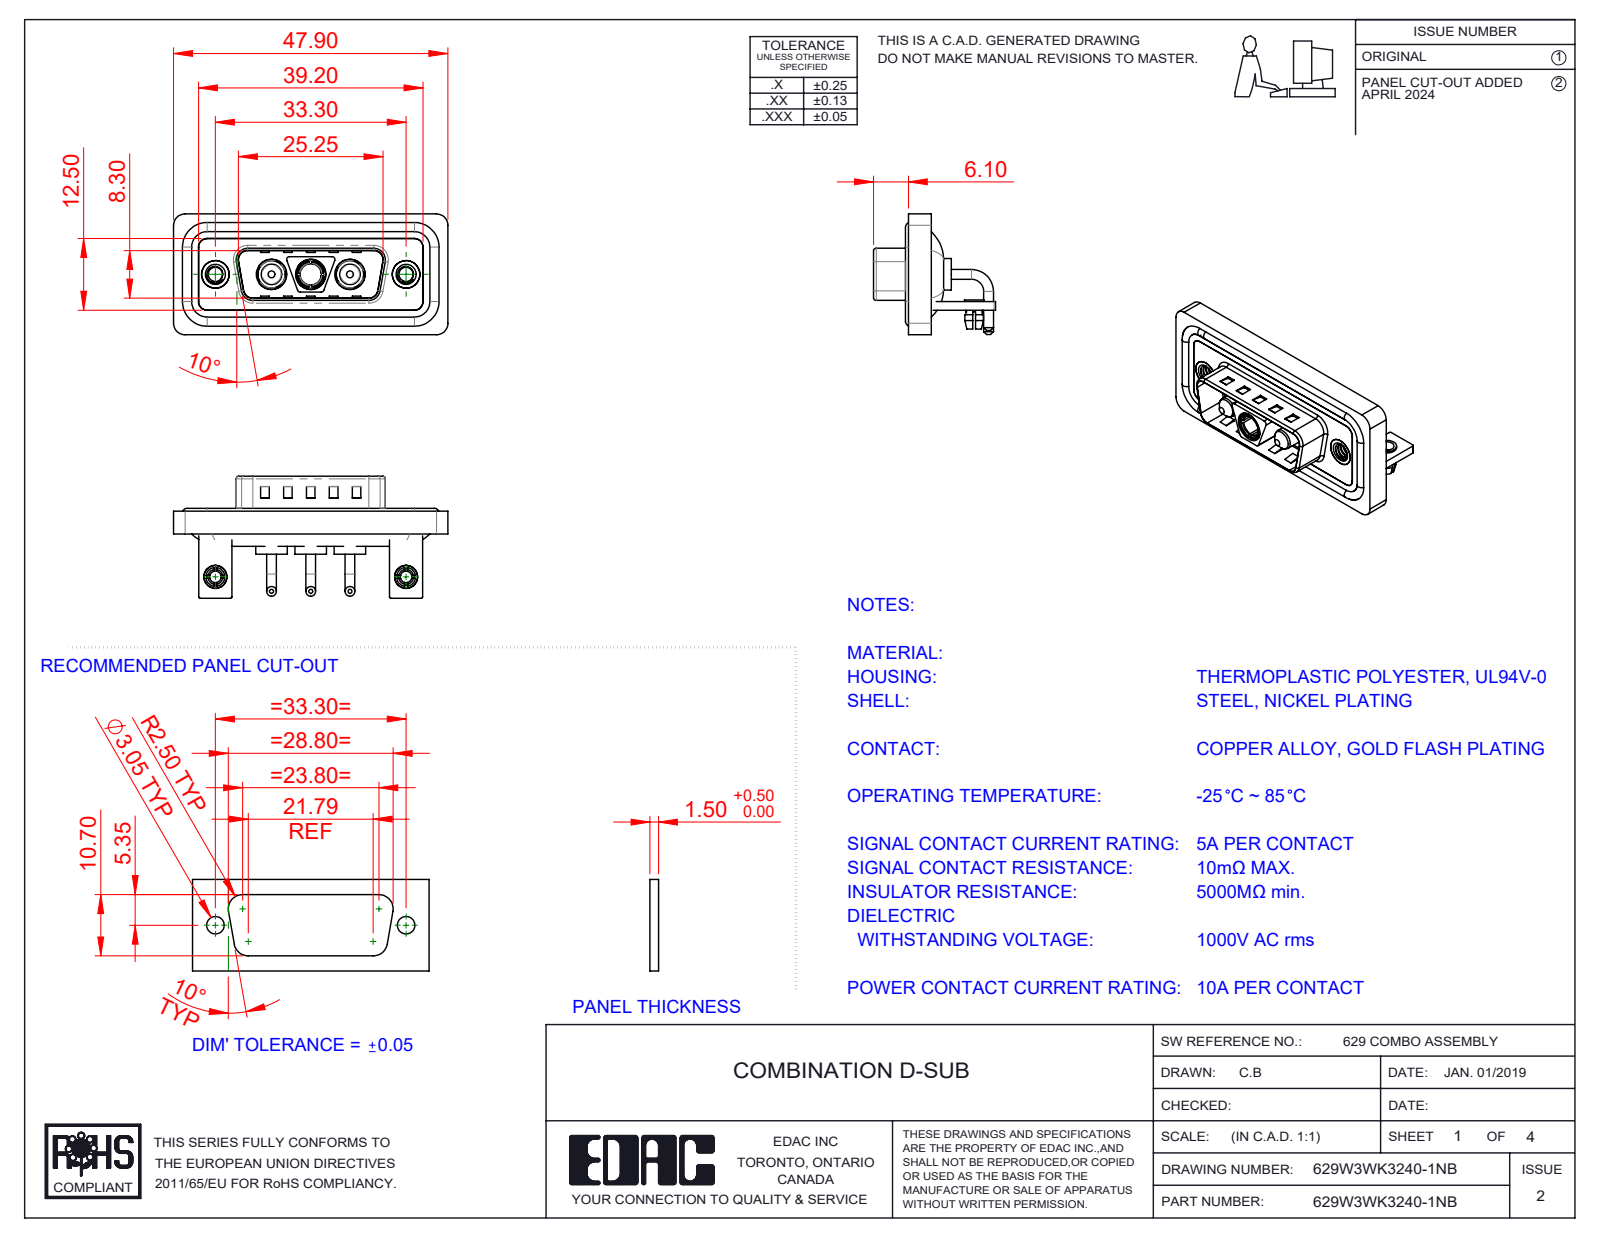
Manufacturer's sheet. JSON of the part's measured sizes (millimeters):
{"part_name": "629Combo Board Lock; Power Pin_10A RA; 629Combo Threaded Rivet_B; 629Combo Housing_3WK3 (+6 more)", "step_written_by": "SolidWorks 2023 (CONFIG_CONTROL_DESIGN)", "units": "millimeters", "bodies": {"solids": 17, "faces": 751, "planar": 299, "cylindrical": 306, "other": 146}, "overall_size": [47.9, 21.3, 21.1], "volume_mm3": 6016, "surface_area_mm2": 10059, "round_holes": [[2.5, 4], [4.85, 3], [5.3, 3], [2, 2], [3.2, 2], [4, 2], [4.8, 2], [5, 2], [3.7, 1]], "round_bosses_or_shafts": [[1.7, 6], [1.6, 4], [5.5, 3], [5.2, 3], [4.75, 3], [3.75, 3], [4.9, 2], [4, 2]], "partial_cylinders_radius": [[2, 21], [1.5, 18], [0.25, 16], [0.5, 13], [1.6, 8], [0.6, 4], [0.65, 4], [0.9, 4]], "face_to_face_distances": [0.4, 1.5, 0.8, 2.9, 1.1, 2.1, 3.7, 1.6, 1.2, 4.5], "hole_center_spacings": [6.85, 9.8, 16.65, 23.5, 33.3, 13.7]}
